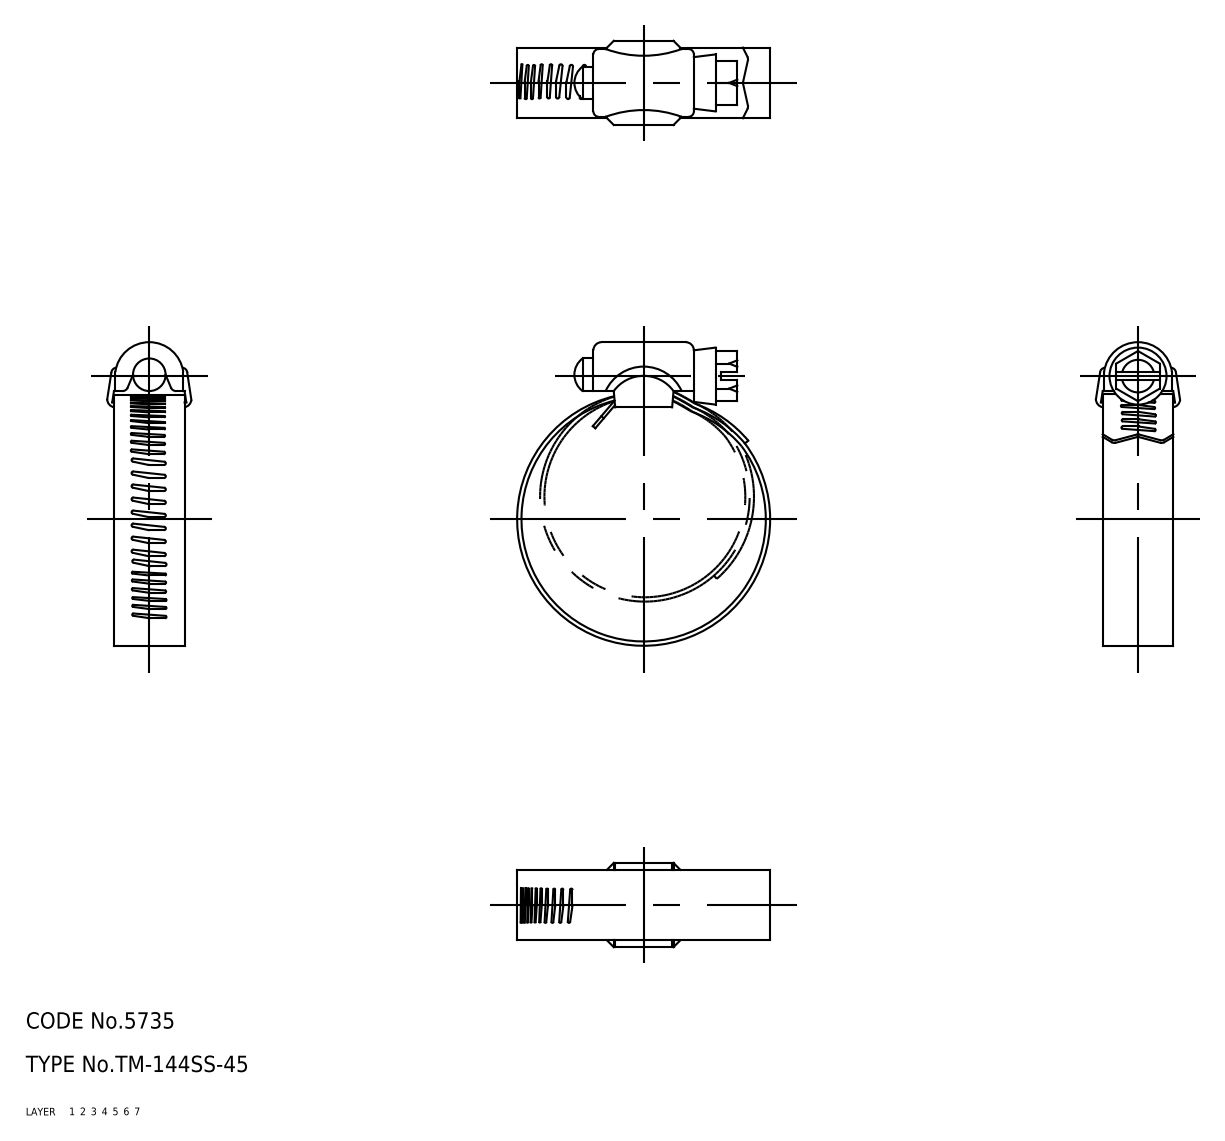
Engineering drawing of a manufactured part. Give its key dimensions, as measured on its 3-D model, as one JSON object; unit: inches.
{"part_name": "screw; holder; band; TM_144SS_45_19949_36", "step_written_by": "CADfix (AUTOMOTIVE_DESIGN)", "units": "inches", "bodies": {"solids": 3, "faces": 215, "planar": 0, "cylindrical": 0, "other": 215}, "overall_size": [2.202, 1.835, 0.615], "volume_in3": 0.24, "surface_area_in2": 10.94}
